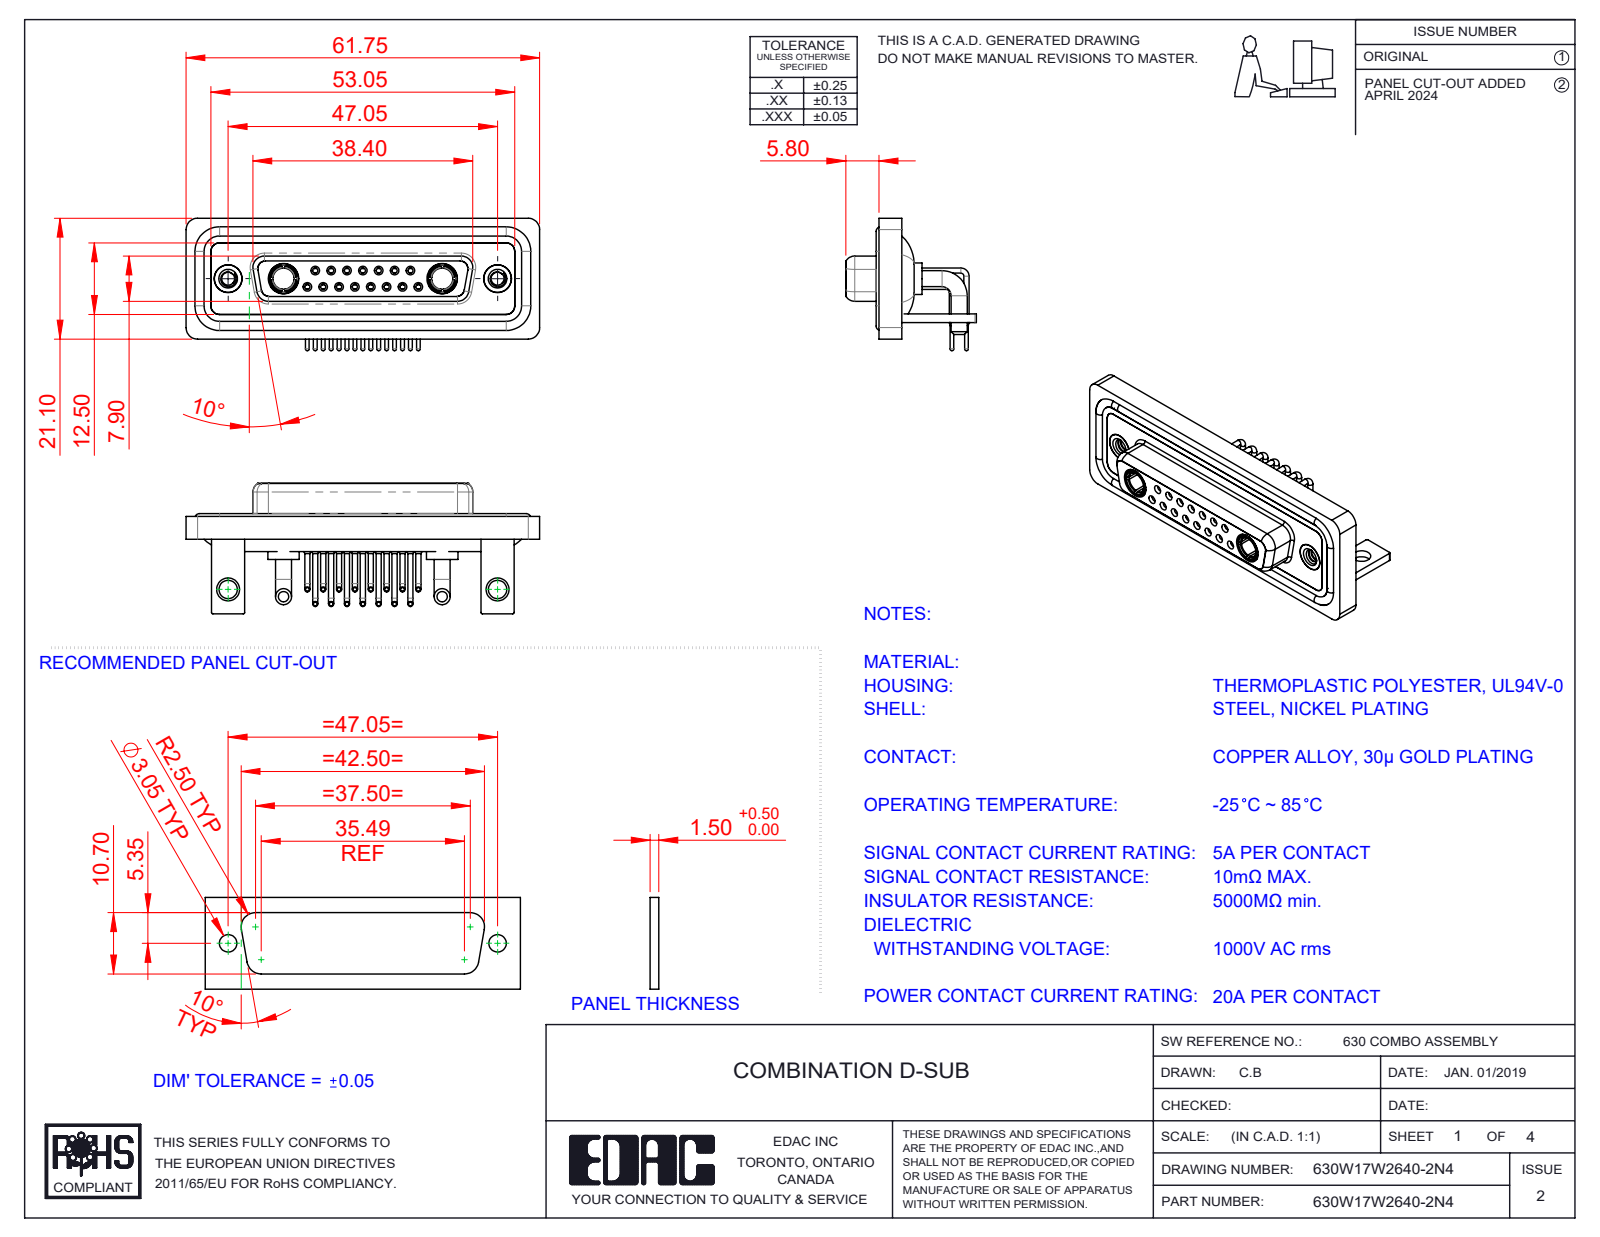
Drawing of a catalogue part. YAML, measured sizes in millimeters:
part_name: "Power Socket_20A RA; 630Combo Shell Front_25 Contacts; 630Combo Contact Row 2_50 Contacts; 630Combo Threaded Rivet_2 (+6 more)"
step_written_by: "SolidWorks 2023 (CONFIG_CONTROL_DESIGN)"
units: millimeters
bodies: {solids: 28, faces: 1385, planar: 408, cylindrical: 607, other: 370}
overall_size: [61.75, 23.12, 22.8]
volume: 8853
surface_area: 15266
round_holes:
  - {diameter: 0.9, count: 15}
  - {diameter: 1.1, count: 15}
  - {diameter: 1.5, count: 15}
  - {diameter: 2, count: 15}
  - {diameter: 1.6, count: 8}
  - {diameter: 1.7, count: 7}
  - {diameter: 4.85, count: 4}
  - {diameter: 2.26, count: 2}
  - {diameter: 3.2, count: 2}
  - {diameter: 3.7, count: 2}
  - {diameter: 4, count: 2}
  - {diameter: 4.05, count: 2}
round_bosses_or_shafts:
  - {diameter: 0.9, count: 15}
  - {diameter: 0.65, count: 15}
  - {diameter: 1.6, count: 11}
  - {diameter: 2.8, count: 4}
  - {diameter: 5.5, count: 2}
  - {diameter: 5.2, count: 2}
  - {diameter: 4.96, count: 2}
  - {diameter: 4.95, count: 2}
partial_cylinders:
  - {radius: 2, count: 19}
  - {radius: 1.5, count: 18}
  - {radius: 0.25, count: 16}
  - {radius: 1.35, count: 8}
  - {radius: 1.6, count: 8}
  - {radius: 0.5, count: 5}
  - {radius: 0.6, count: 4}
  - {radius: 0.65, count: 4}
face_to_face_distances: [0.4, 1.8, 2.9, 3.7, 1.5, 4.1, 1.1, 1.4, 1.6, 3.1]
hole_center_spacings: [3.16, 2.77, 5.54, 8.31, 5.04, 7.49, 11.08, 5.03]
